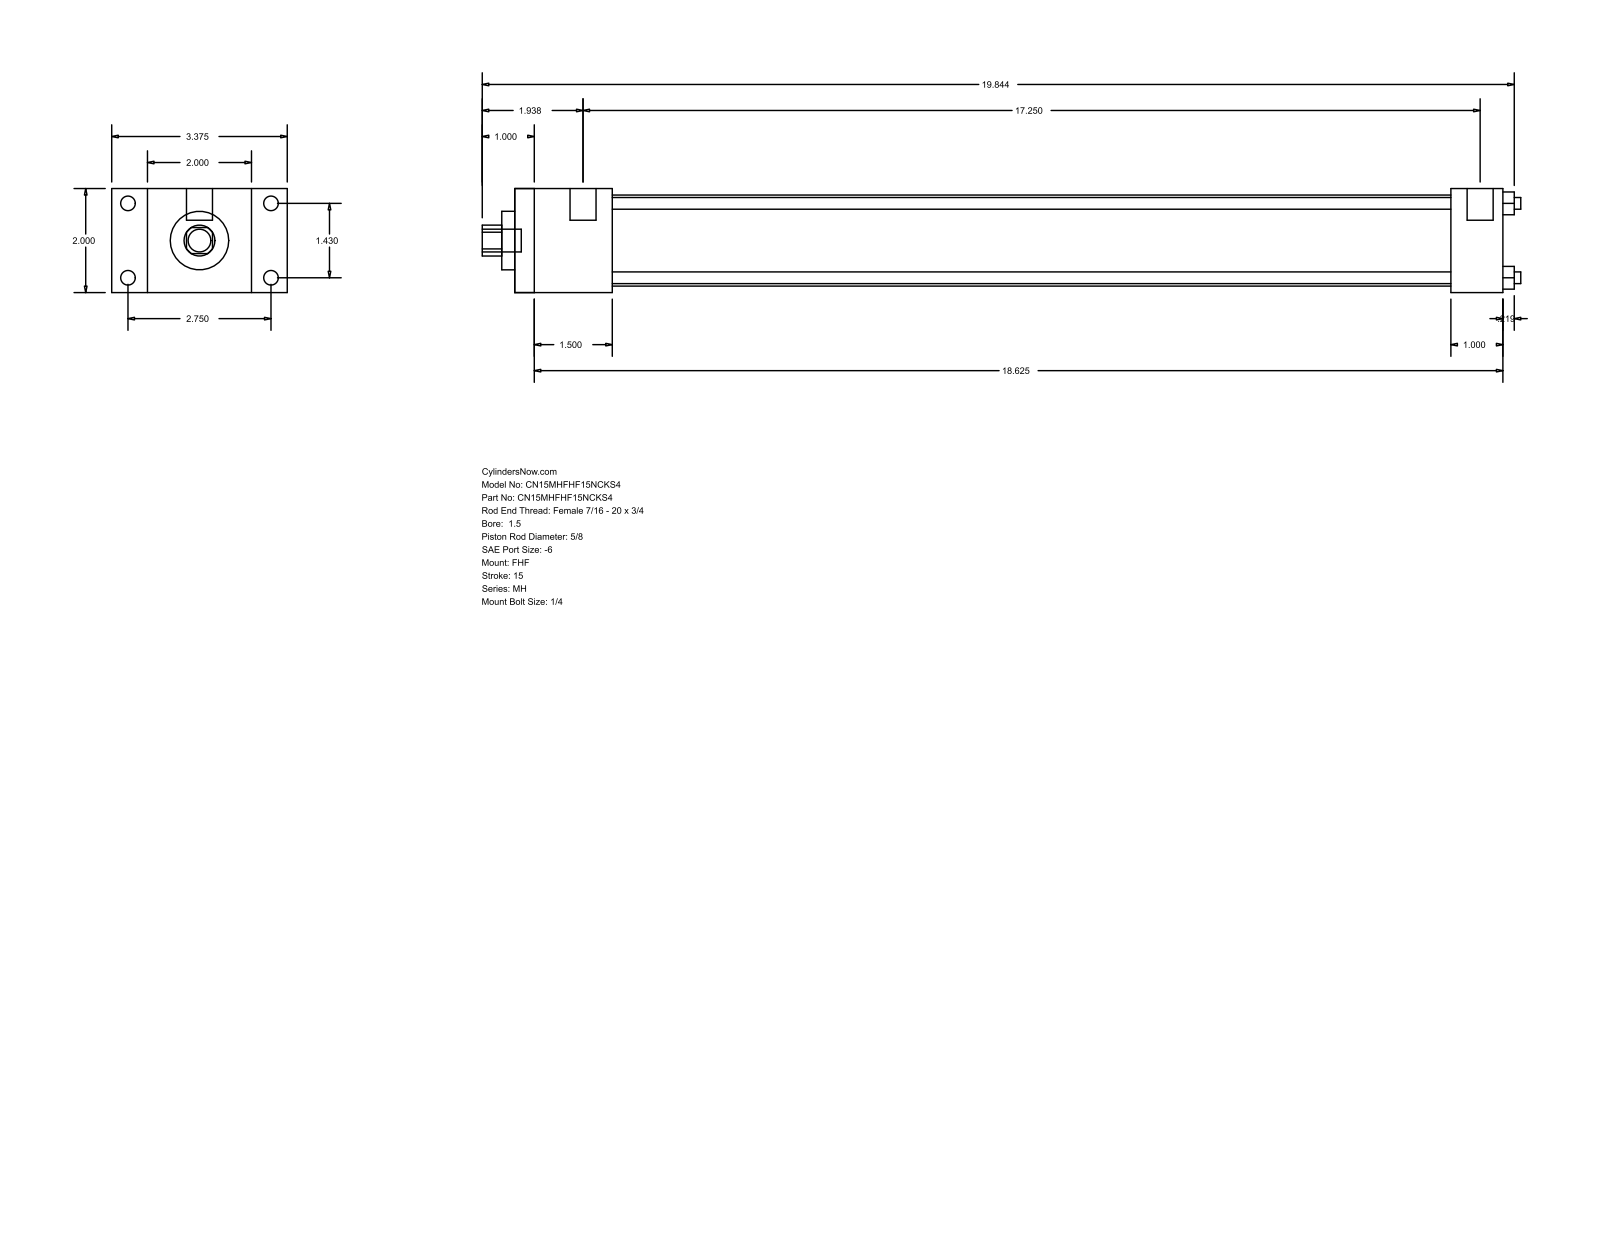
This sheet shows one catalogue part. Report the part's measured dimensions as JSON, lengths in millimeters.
{"part_name": "MH_FHF__0150_0.625", "step_written_by": "GSSL Pune (CONFIG_CONTROL_DESIGN)", "units": "millimeters", "bodies": {"solids": 0, "faces": 88, "planar": 60, "cylindrical": 28, "other": 0}, "overall_size": [507.21, 85.72, 50.8], "round_holes": [[5.71, 4], [15.88, 1], [28.57, 1], [44.45, 1]], "round_bosses_or_shafts": [[7.14, 4], [5.56, 4], [12.7, 2], [11.11, 1]], "partial_cylinders_radius": [[7.54, 1]], "face_to_face_distances": [50.8, 17.46, 68.26, 47.62, 85.72, 482.6, 434.98, 457.19, 409.57, 25.41], "hole_center_spacings": [25.68, 36.32, 51.36]}
